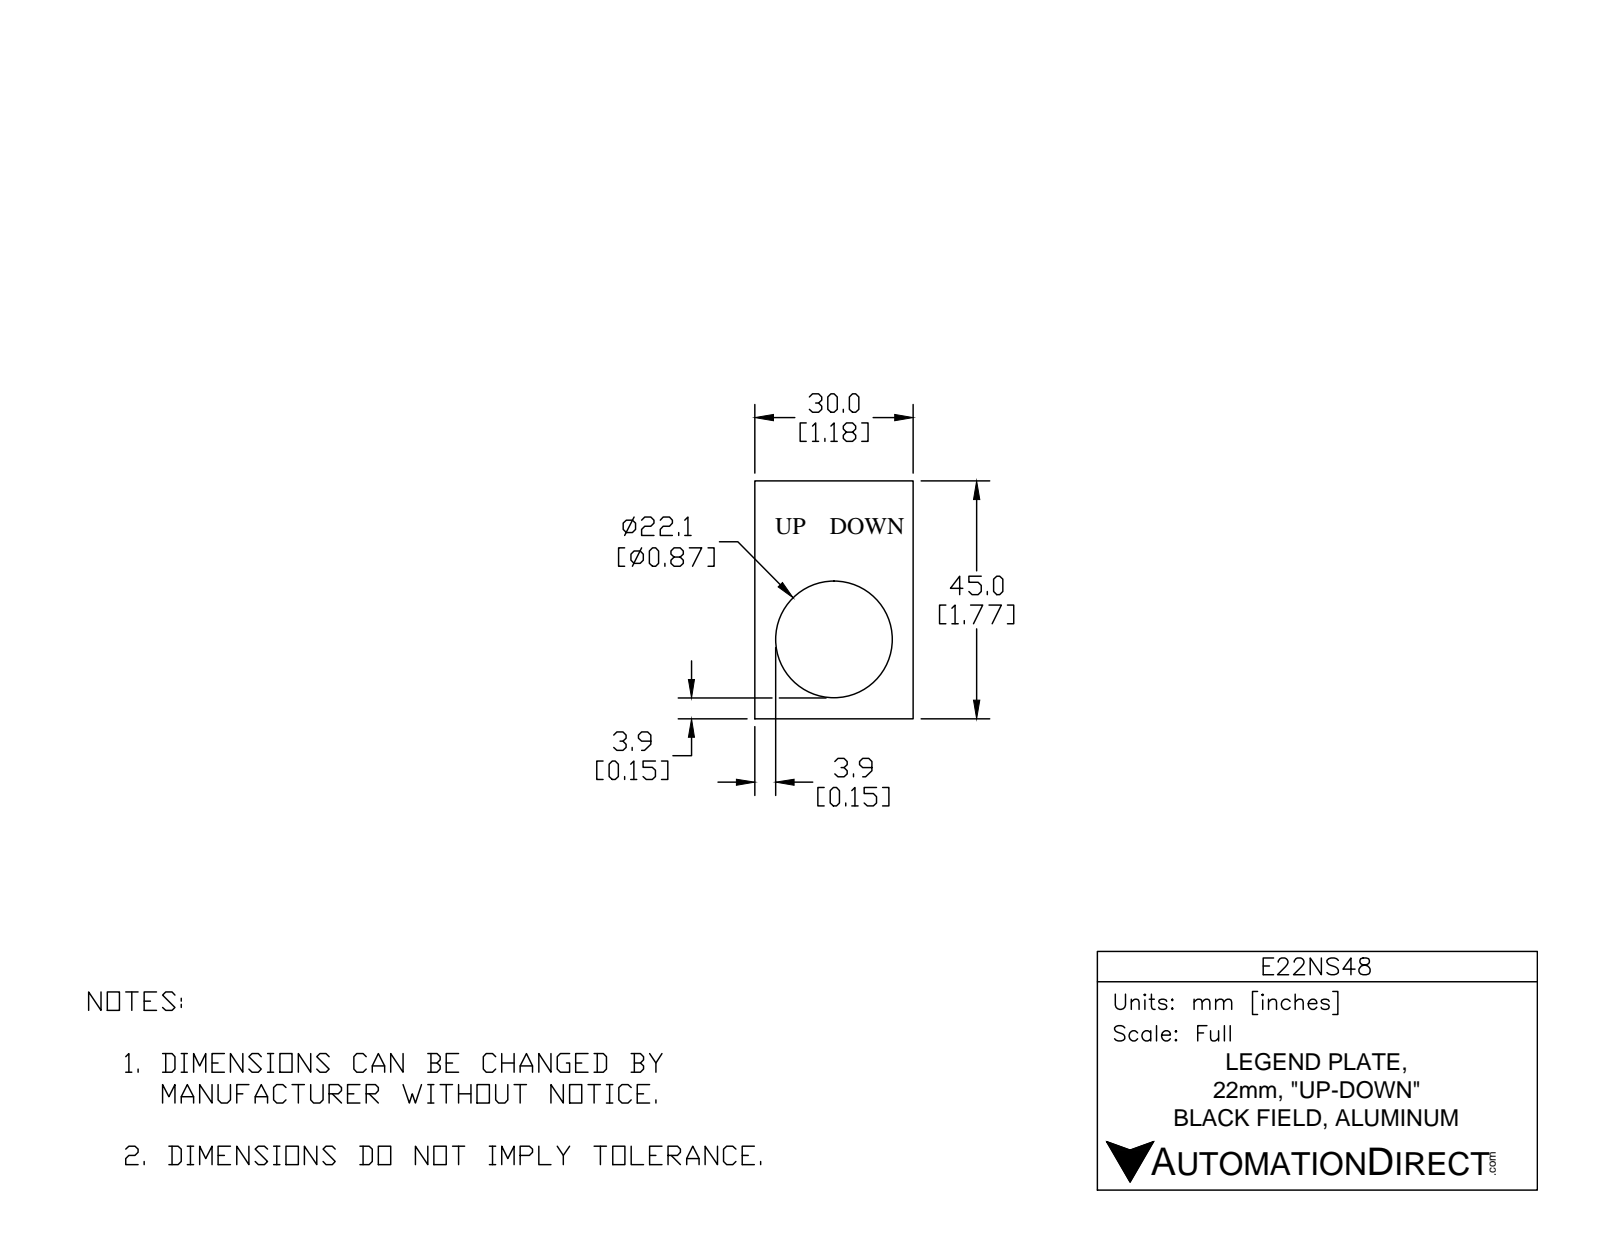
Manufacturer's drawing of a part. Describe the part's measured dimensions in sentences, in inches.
The part is named "E22NS48". Its 3-D file was written by "SolidWorks 2017 (AUTOMOTIVE_DESIGN)". It is 1 solid with 97 faces: 66 planar, 3 cylindrical and 28 other. Overall it measures 1.772 by 1.181 by 0.051 inches. Its volume is 0.076 cubic inches and its surface area 3.481 square inches. Round holes: 1 of diameter 0.874. The main face-to-face distances are 0.051, 1.181, 1.772, 0.041, 0.185, 1.587, 0.528, 0.654, 0.16, 0.187.
